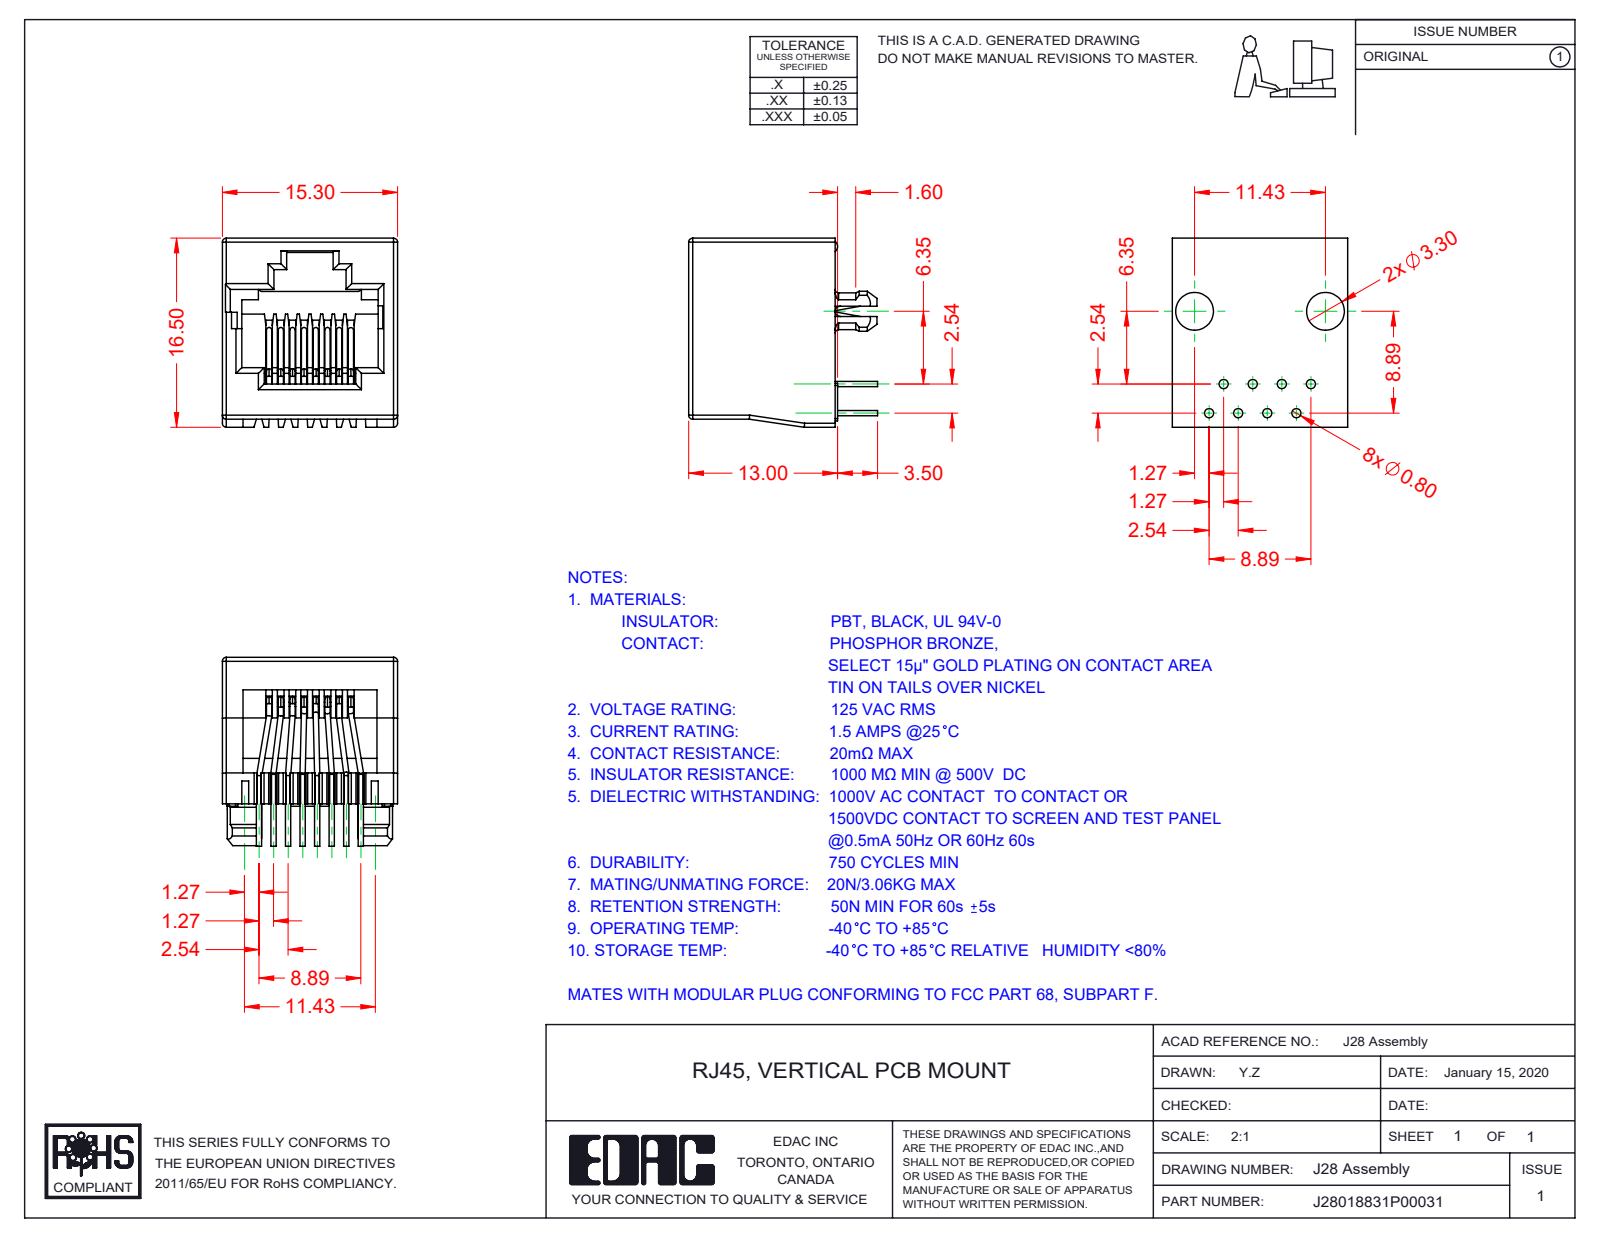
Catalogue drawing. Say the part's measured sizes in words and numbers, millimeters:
The part is named "28 Insulator; 28 Contacts; RJ28018831P00031". Its 3-D file was written by "SolidWorks 2016 (CONFIG_CONTROL_DESIGN)". It is 9 solids with 580 faces: 319 planar, 205 cylindrical and 56 other. Overall it measures 16.5 by 16.5 by 15.3 millimeters. Its volume is 1 535 cubic millimeters and its surface area 2 745 square millimeters. Round holes: 2 of diameter 1.6. Round bosses or shafts: 45 of diameter 0.46. Partial cylindrical surfaces (rounded edges, fillets, slot ends): 19 of radius 0.5, 16 of radius 0.1, 14 of radius 0.35, 10 of radius 0.25, 8 of radius 0.2, 8 of radius 0.23, 2 of radius 0.45, 2 of radius 1.6. The main face-to-face distances are 15.3, 1.02, 1.7, 13.6, 1.25, 2.04, 12.81, 3.06, 3.15, 12.15. The hole center spacings are 12.
